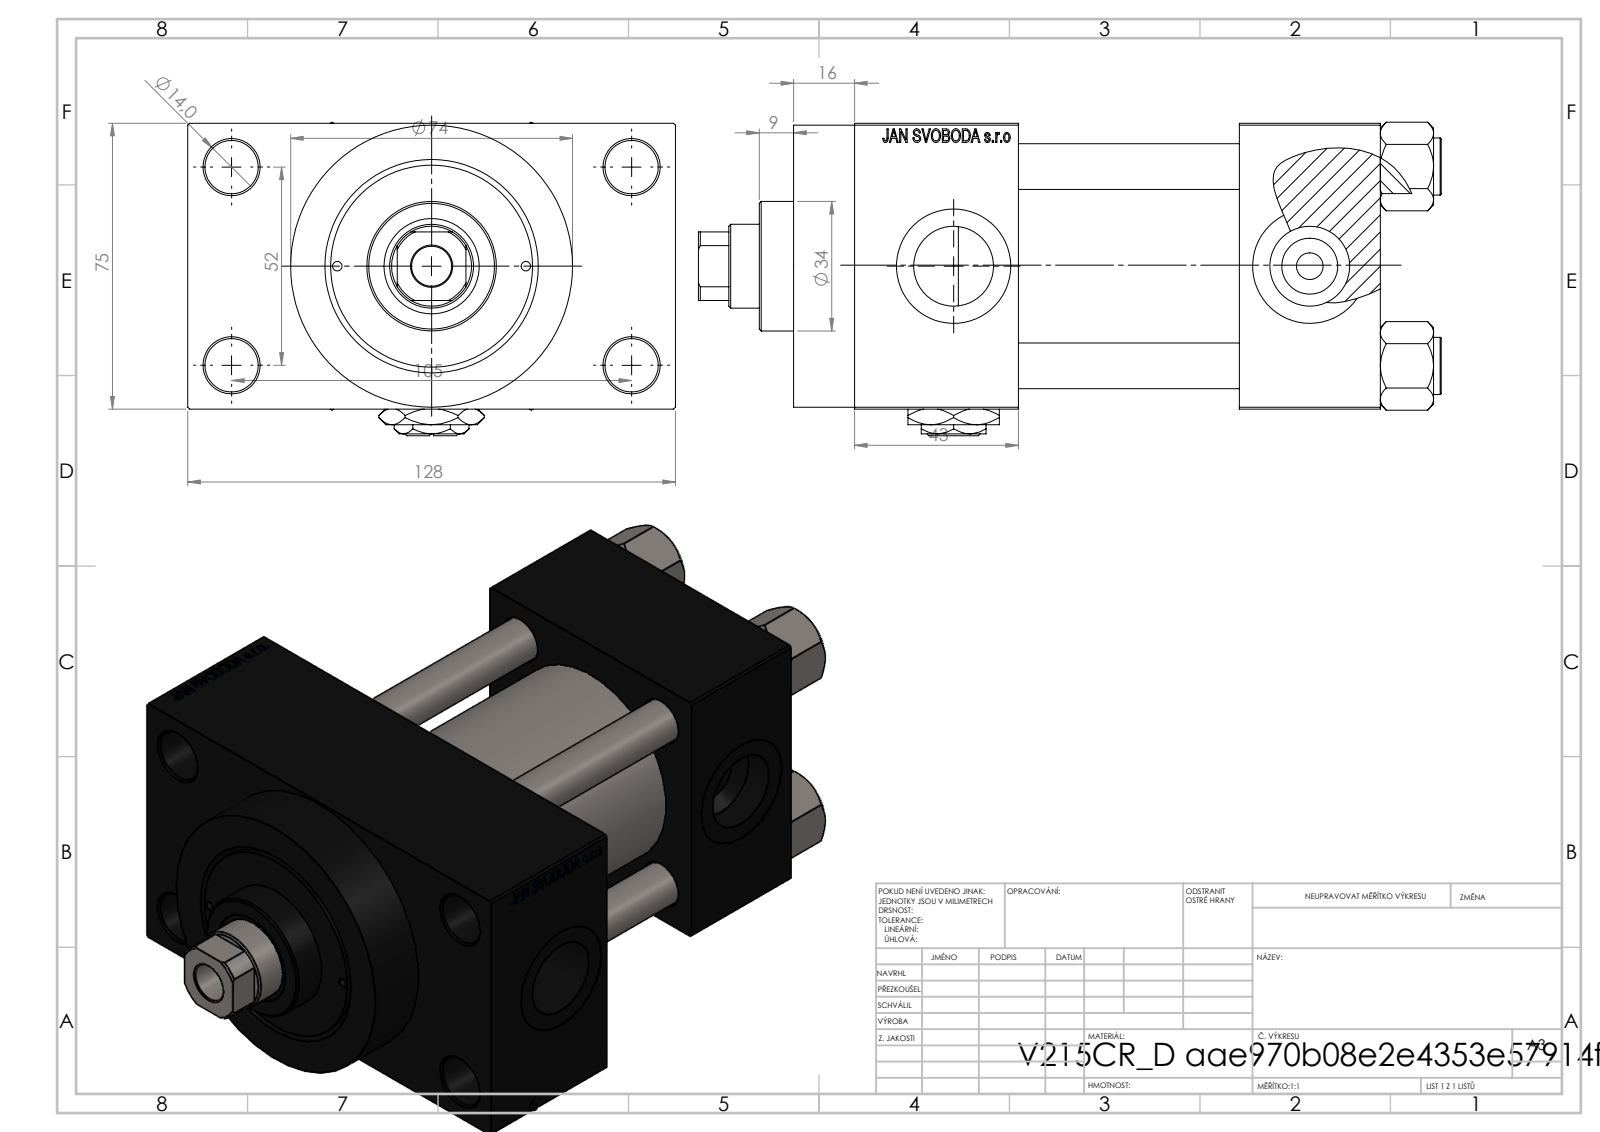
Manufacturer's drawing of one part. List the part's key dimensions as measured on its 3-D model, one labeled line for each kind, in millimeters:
Part name (STEP PRODUCT): V215CR_D_Body; V215CR_VCP_D; Zatka_pro_OIL_PORT; V215_VC_A (+2 more)
STEP written by: SolidWorks 2019 (CONFIG_CONTROL_DESIGN)
Units: millimetres
Bodies: 12 solids, 1159 faces (523 planar, 96 cylindrical, 540 other)
Overall size (bounding box): 195 × 128 × 82.27
Volume: 795 436 mm³ · Surface area: 168 140 mm²
Round holes (diameter × count): ⌀12 ×4, ⌀14 ×4, ⌀20.96 ×3, ⌀30 ×3, ⌀2.5 ×2, ⌀7 ×2, ⌀10.5 ×1, ⌀22 ×1, ⌀25 ×1, ⌀41 ×1, ⌀50 ×1, ⌀53 ×1
Round bosses / shafts (diameter × count): ⌀15 ×4, ⌀74 ×1, ⌀56 ×1, ⌀34 ×1
Partial cylindrical surfaces — rounded edges, fillets, slot ends (radius × count): R10.5 ×1
Main face-to-face distances: 75, 58, 37, 95, 26.5, 138, 101, 43, 101.5, 16
Hole centre spacings: 26.19, 26.35, 36.98, 38.03, 52.3, 57.22, 58.43, 58.59
